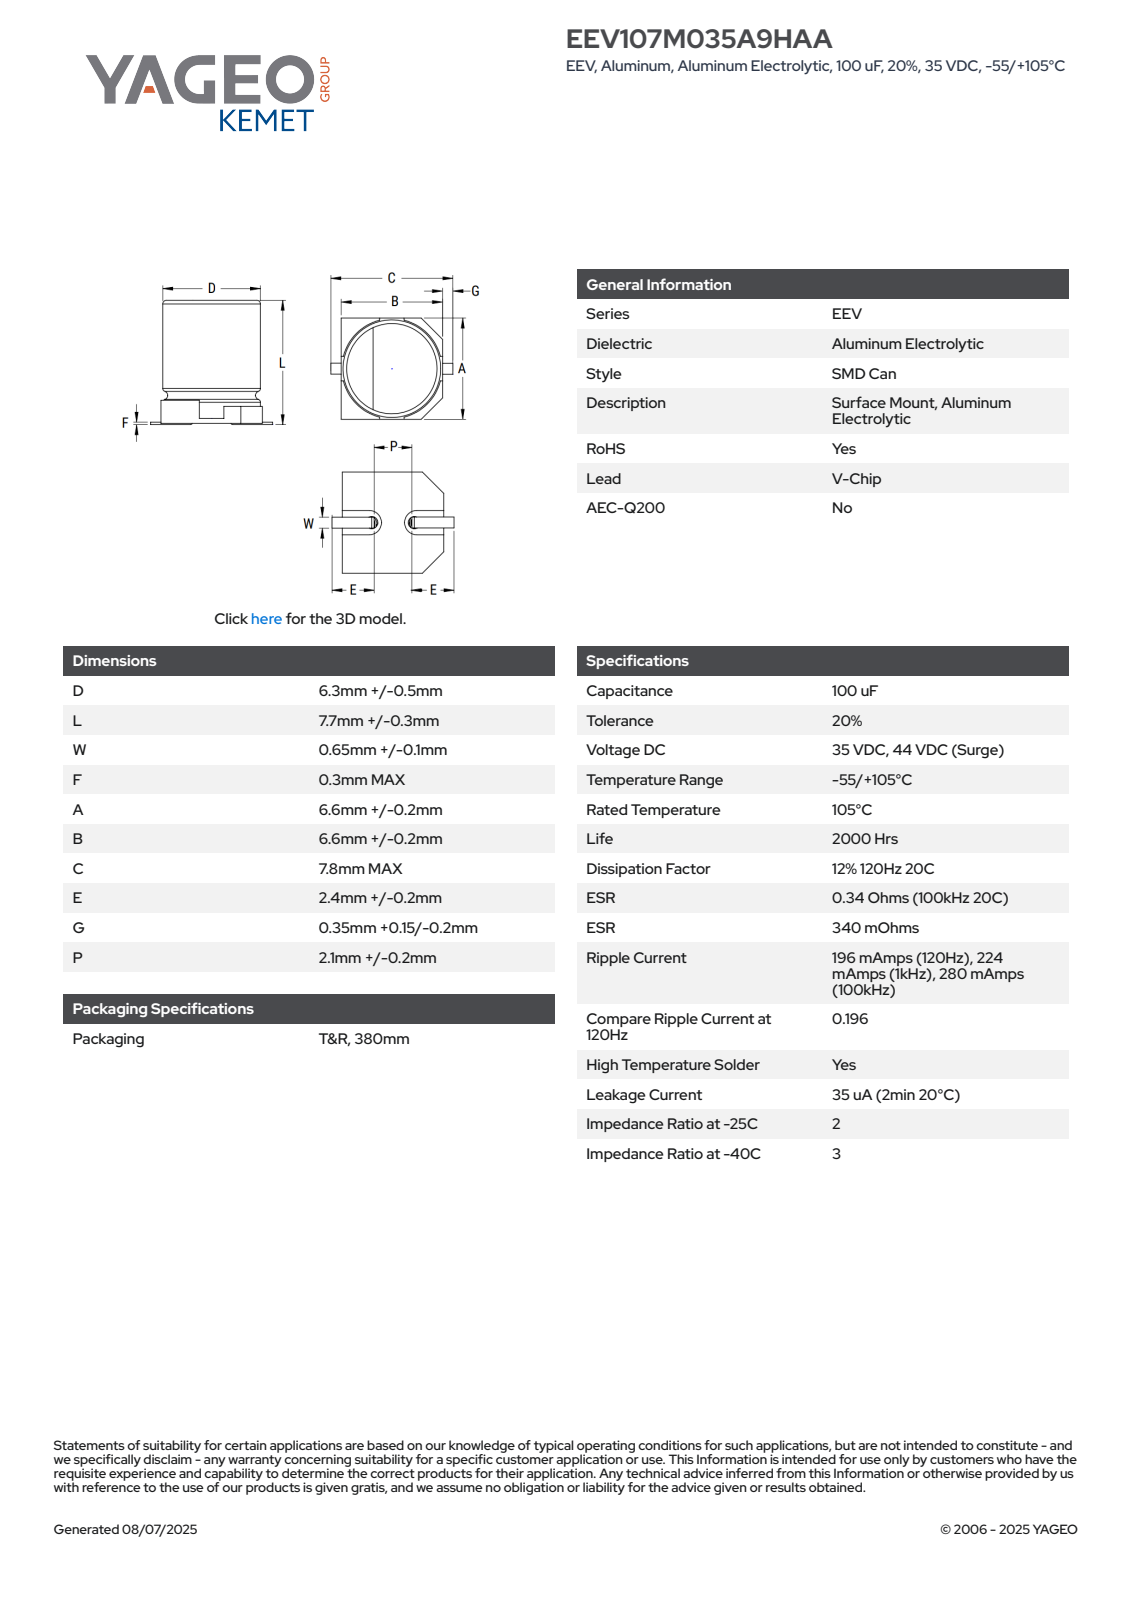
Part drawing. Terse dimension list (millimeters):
name: CAC_S_6.3X7.7_D6.8L8W0.75F0.3A6.8B6.8C7.8E2.8P2
written by: SolidWorks 2021 (AUTOMOTIVE_DESIGN)
unit: mm
bodies: 5 solids, 78 faces (61 planar, 11 cylindrical, 6 other)
size: 8.01 × 7.5 × 6.8
volume: 266 mm³; area: 359 mm²
bosses: 1× ⌀6.5
rounds: 2× R0.2, 1× R2.7, 1× R3.4
face distances: 0.4, 7.7, 7.3, 7.71, 7.31, 6.8, 2, 1.6, 5.7, 5.71
